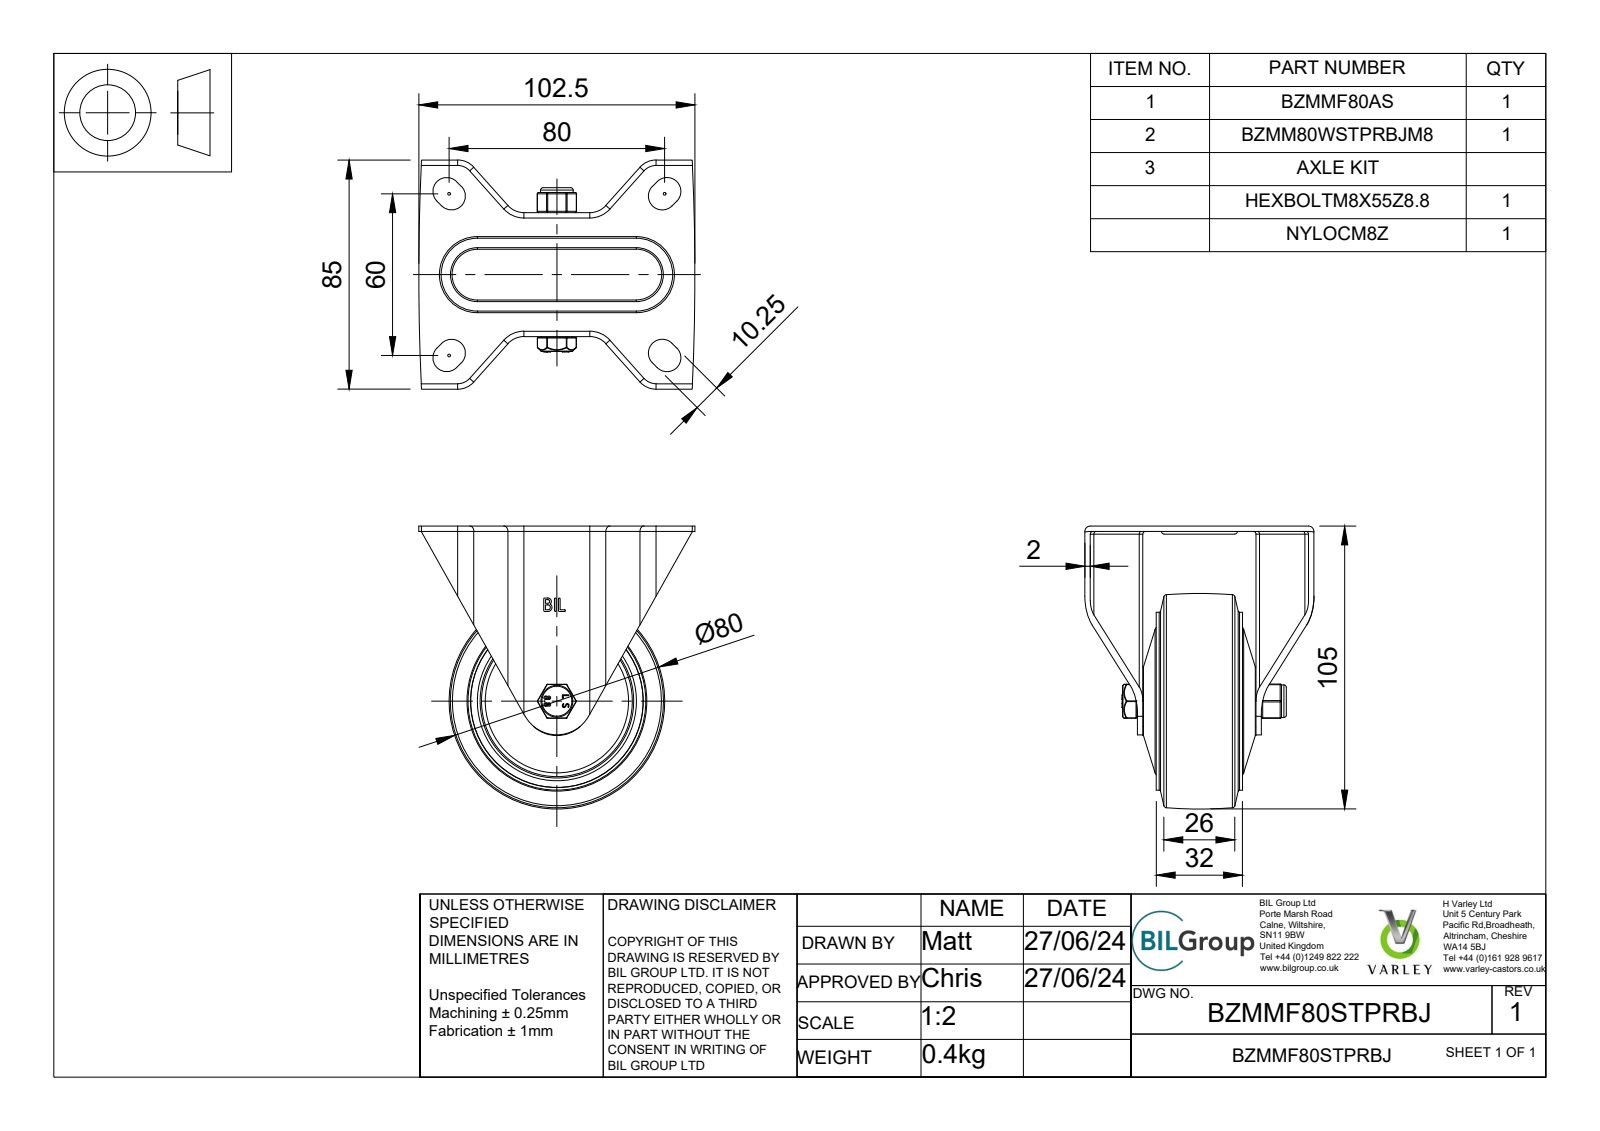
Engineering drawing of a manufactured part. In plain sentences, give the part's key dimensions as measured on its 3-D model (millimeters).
The part is named "BZMMF80STPRBJ v3; BZMMF80AS - 42 v2; ZINC PLATED, PRESSED STEEL BRACKET; BZMM80WSTPRBJM8 v1 (+7 more)". Its 3-D file was written by "Autodesk Translation Framework v13.14.0.145 (AUTOMOTIVE_DESIGN)". It is 21 solids with 785 faces: 275 planar, 224 cylindrical and 286 other. Overall it measures 105 by 102.5 by 85 millimeters. Its volume is 143 574 cubic millimeters and its surface area 106 271 square millimeters. Round holes: 2 of diameter 0.66, 1 of diameter 8, 1 of diameter 8.25, 1 of diameter 8.5, 1 of diameter 8.6, 1 of diameter 20, 1 of diameter 22.5, 1 of diameter 30, 1 of diameter 31, 1 of diameter 32, 1 of diameter 32.5, 1 of diameter 35. Round bosses or shafts: 1 of diameter 66, 1 of diameter 56, 1 of diameter 43, 1 of diameter 39, 1 of diameter 34.5, 1 of diameter 30.5, 1 of diameter 25.5, 1 of diameter 23. Partial cylindrical surfaces (rounded edges, fillets, slot ends): 18 of radius 0.5, 12 of radius 0.25, 12 of radius 1, 8 of radius 2, 8 of radius 4, 8 of radius 5.12, 8 of radius 8, 4 of radius 0.33. The main face-to-face distances are 2, 44, 5.16, 21, 42, 46, 25, 19, 23, 17.5. The hole center spacings are 3.22, 2.49.
